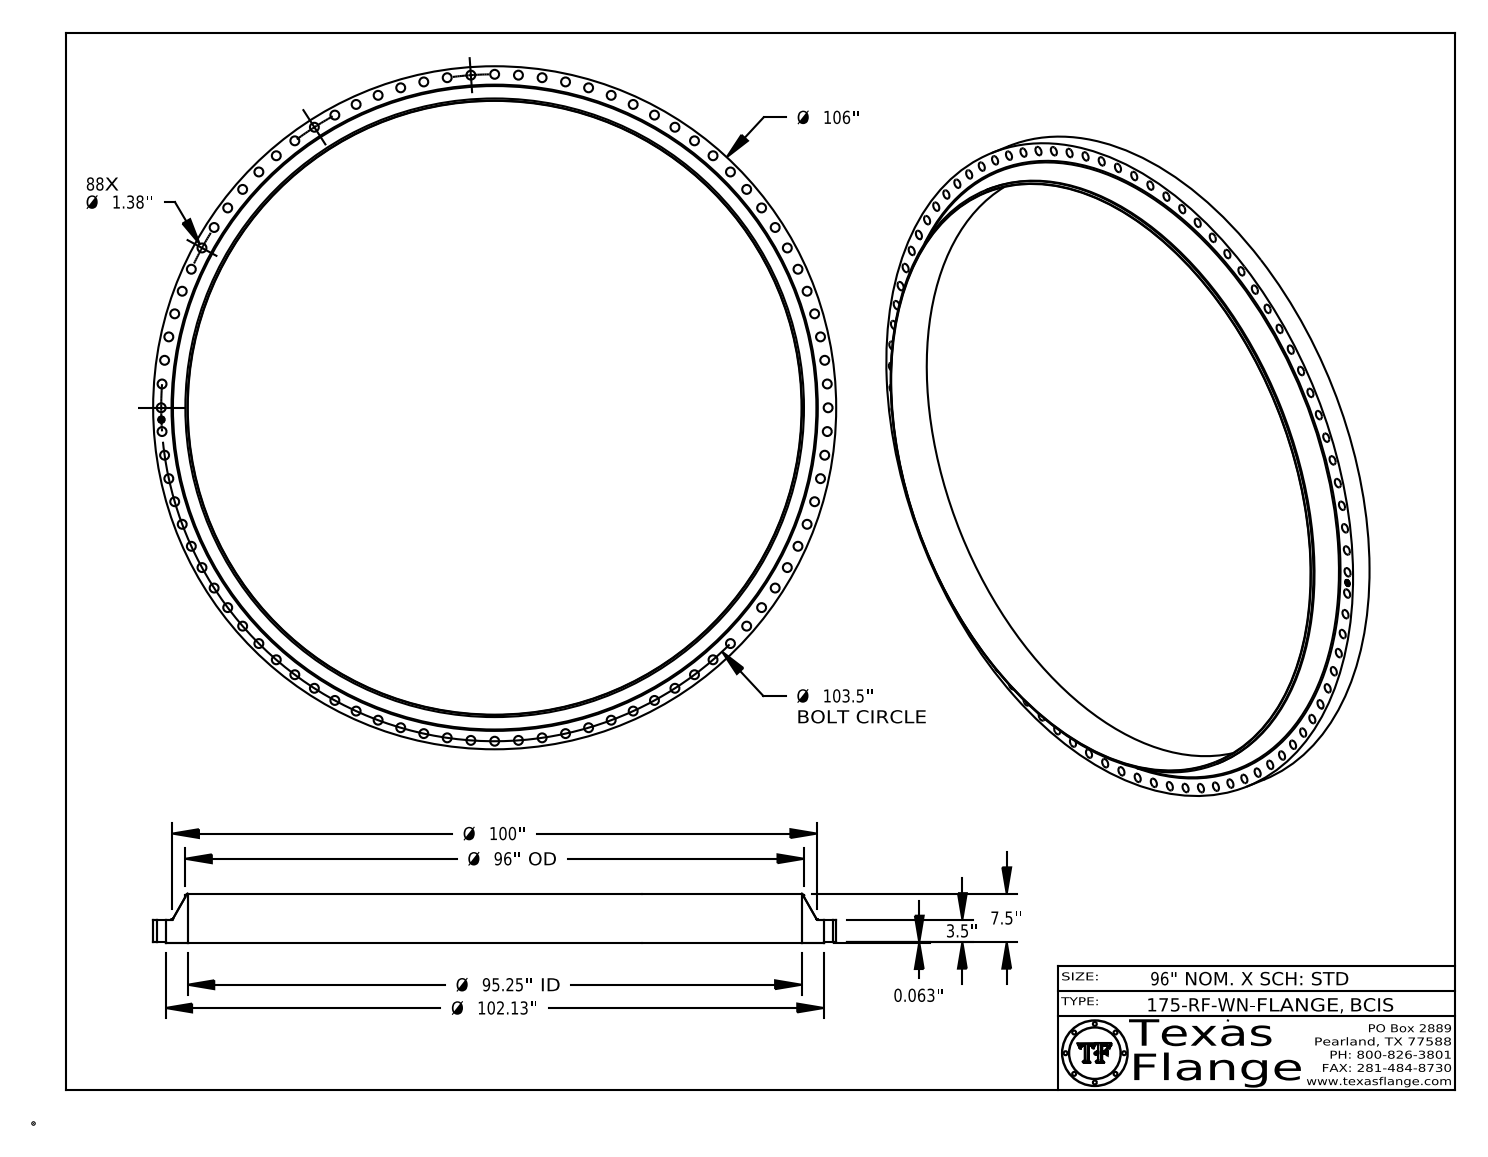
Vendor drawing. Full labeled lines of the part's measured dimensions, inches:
Part name (STEP PRODUCT): 175-RF-WN, BCIS
STEP written by: CATIA V5 STEP AP214 (AUTOMOTIVE_DESIGN)
Units: inches
Bodies: 1 solid, 665 faces (369 planar, 290 cylindrical, 6 other)
Overall size (bounding box): 106 × 106 × 7.563
Volume: 7 071 in³ · Surface area: 8 638 in²
Round holes (diameter × count): ⌀1.38 ×88, ⌀1 ×1, ⌀95.25 ×1
Round bosses / shafts (diameter × count): ⌀0.061 ×8, ⌀106 ×1, ⌀102.13 ×1, ⌀96 ×1, ⌀0.788 ×1
Main face-to-face distances: 3.563, 0.063, 3.5, 7.563, 7.5, 4, 0.015, 3.548, 3.485, 4.015
Hole centre spacings: 51.75, 3.694, 18.377, 22, 11.064, 32.685, 96.974, 7.383
